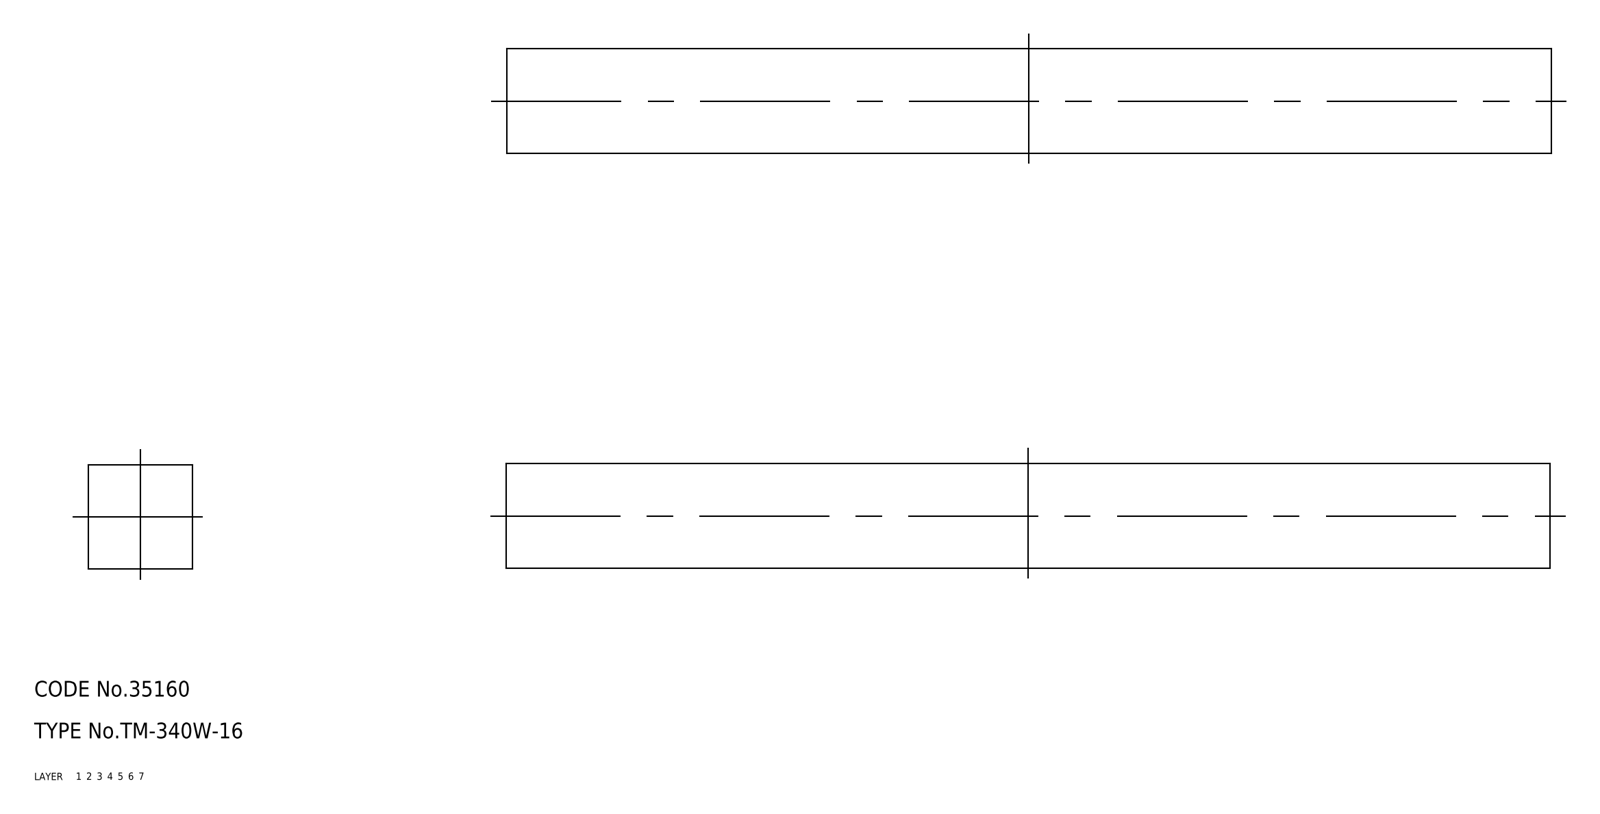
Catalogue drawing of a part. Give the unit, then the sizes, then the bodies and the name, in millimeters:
Units: millimetres
Overall size (bounding box): 200 × 20 × 20
Main face-to-face distances: 20, 200
Volume: 80 000 mm³ · Surface area: 16 800 mm²
Bodies: 1 solid, 6 faces (6 planar, 0 cylindrical, 0 other)
Part name (STEP PRODUCT): rubber foam; TM_340W_16
STEP written by: SolidWorks 2015 (AUTOMOTIVE_DESIGN)
